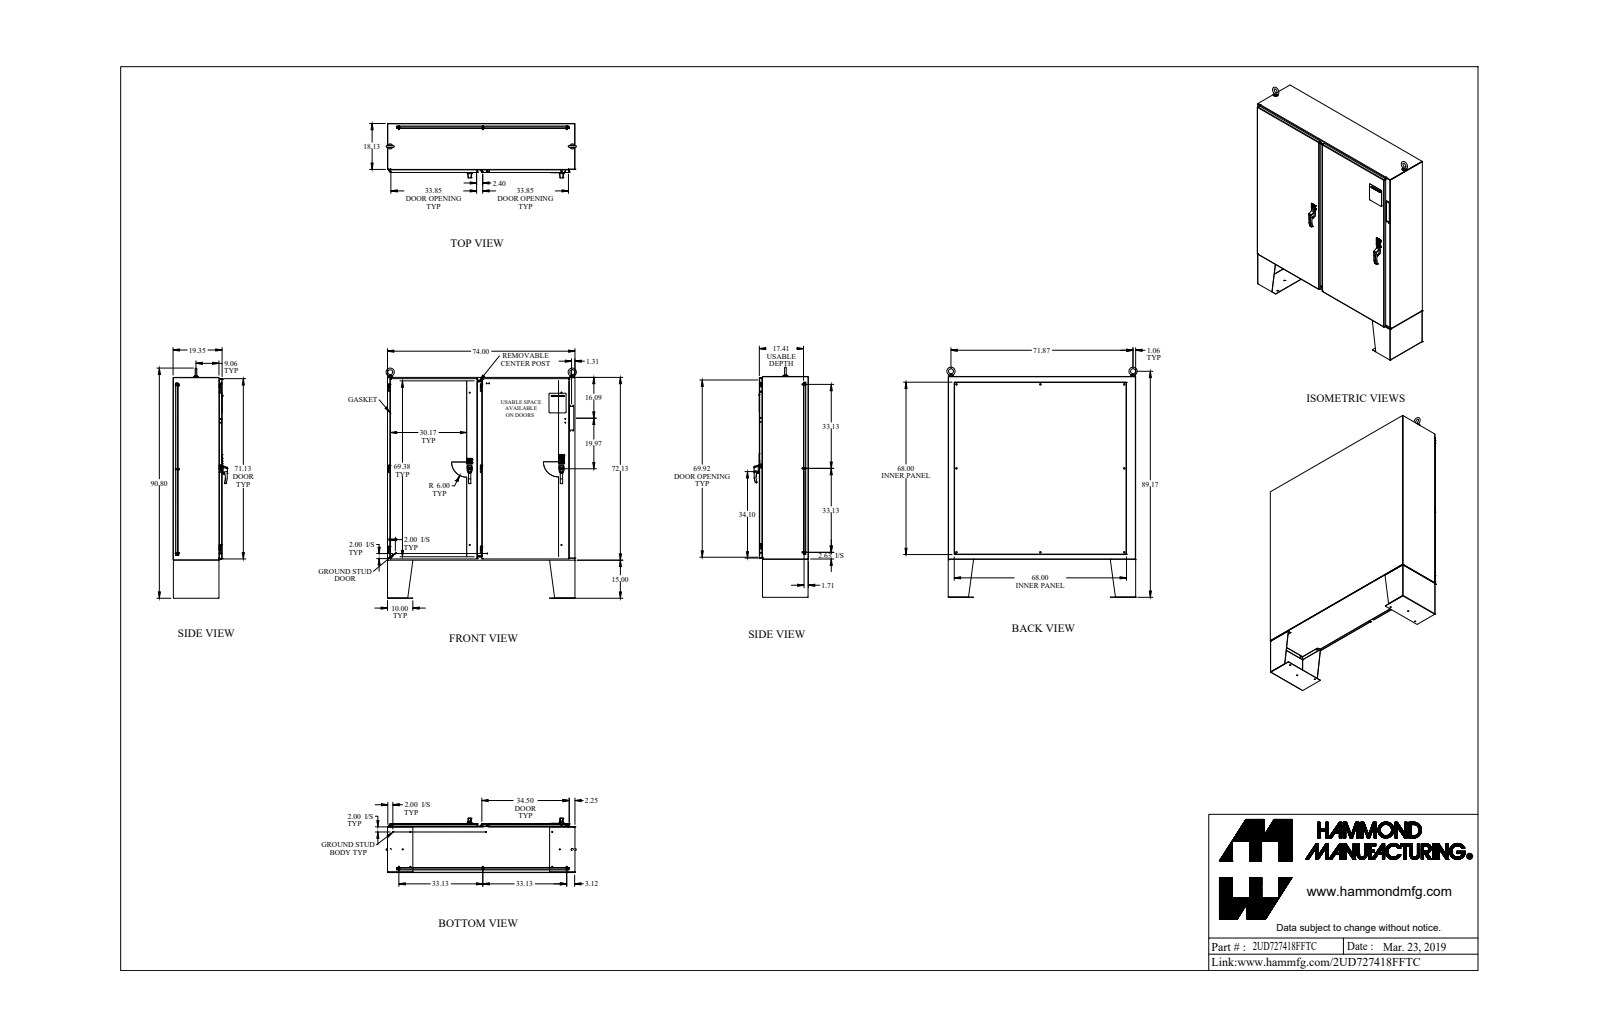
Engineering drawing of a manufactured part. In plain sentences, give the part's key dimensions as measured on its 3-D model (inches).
The part is named "2UD727418FFTC". Its 3-D file was written by "SolidWorks 2018 (AUTOMOTIVE_DESIGN)". It is 214 solids with 3142 faces: 1822 planar, 934 cylindrical and 386 other. Overall it measures 90.799 by 75.122 by 21.466 inches. Its volume is 4 939 cubic inches and its surface area 52 193 square inches. Round holes: 14 of diameter 0.437, 11 of diameter 0.281, 11 of diameter 0.307, 10 of diameter 0.196, 10 of diameter 0.25, 8 of diameter 0.35, 6 of diameter 0.257, 6 of diameter 0.313, 5 of diameter 0.445, 4 of diameter 0.28, 4 of diameter 0.282, 4 of diameter 0.375. Round bosses or shafts: 19 of diameter 0.25, 14 of diameter 1, 9 of diameter 0.65, 9 of diameter 0.375, 9 of diameter 0.33, 8 of diameter 0.281, 6 of diameter 0.75, 6 of diameter 0.53. Partial cylindrical surfaces (rounded edges, fillets, slot ends): 62 of radius 0.125, 51 of radius 0.06, 38 of radius 0.5, 32 of radius 0.017, 30 of radius 0.185, 28 of radius 0.03, 20 of radius 0.048, 20 of radius 0.143. The main face-to-face distances are 0.125, 0.072, 17.431, 19.368, 19.243, 1.937, 1.812, 1.741, 1.865, 17.503. The hole center spacings are 1, 36.25, 7.487, 8.126, 8.675, 16.065, 59.398, 64.126.
